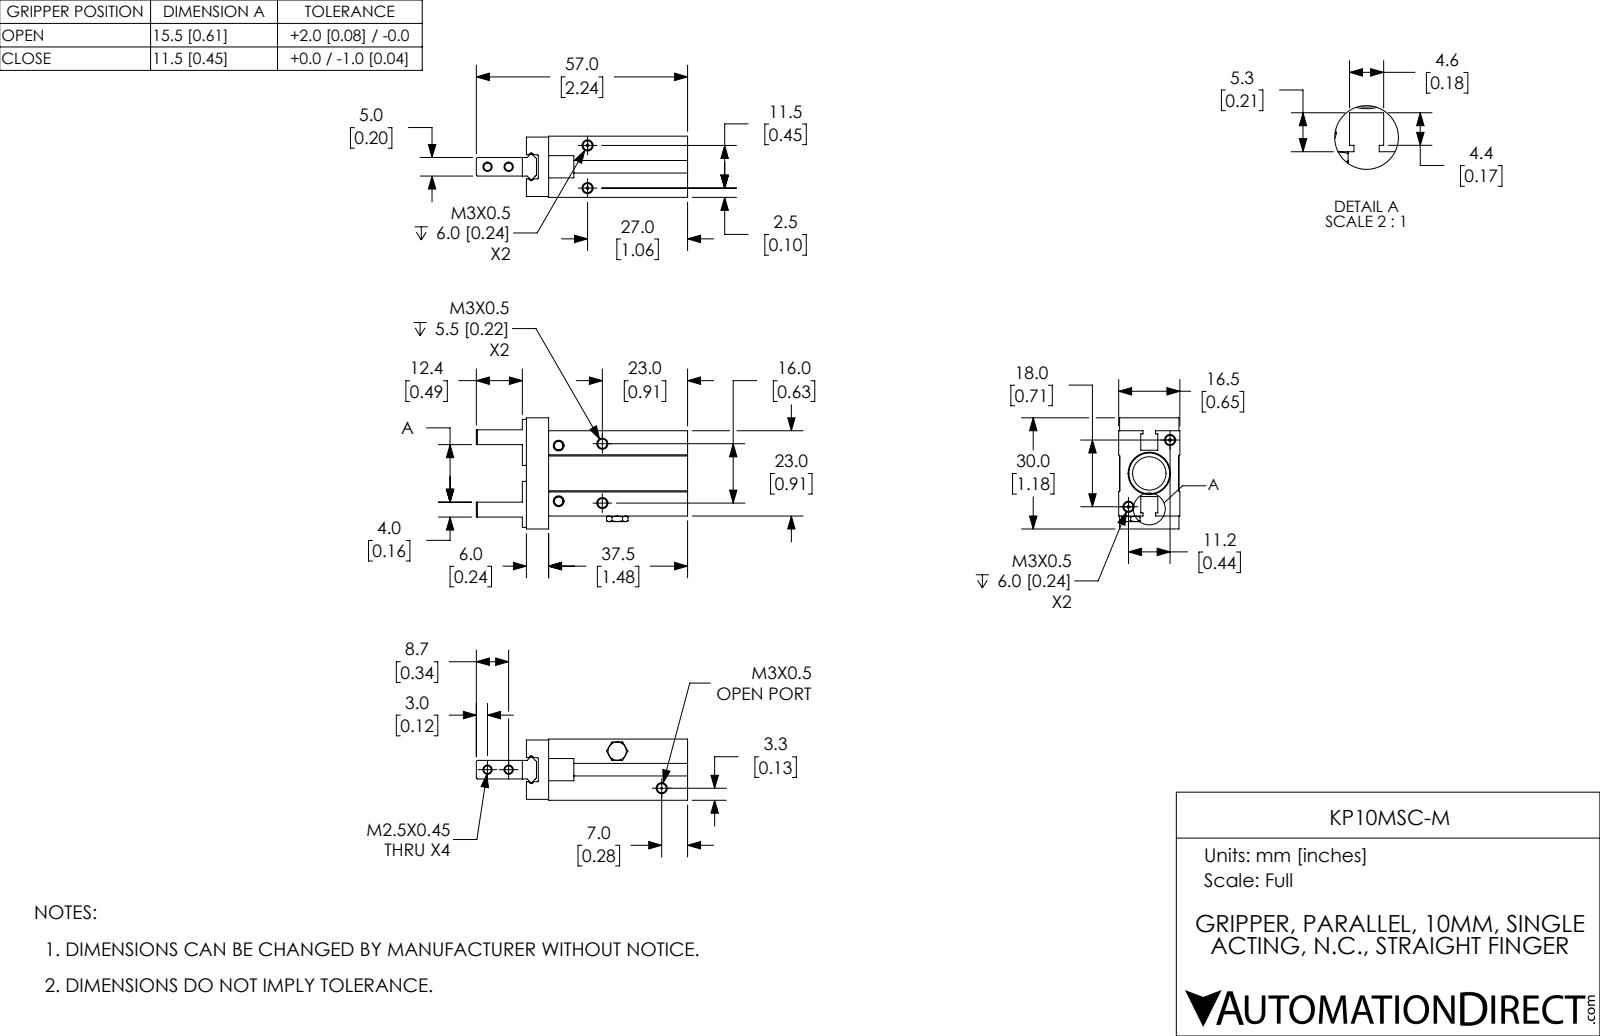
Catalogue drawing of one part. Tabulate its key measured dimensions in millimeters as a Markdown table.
| quantity | value |
| --- | --- |
| part name | KP10MSC-M; KP10MSC-M-3; KP10MSC-M-2; KP10MSC-M-1 |
| STEP written by | SolidWorks 2017 (CONFIG_CONTROL_DESIGN) |
| units | millimeters |
| bodies | 3 solids, 240 faces (118 planar, 56 cylindrical, 66 other) |
| overall size | 57 × 30 × 16.5 |
| volume | 14 374 mm³ |
| surface area | 7 494 mm² |
| round holes (diameter × count) | 2.46 × 4, 2.46 × 4, 0.5 × 2, 2.01 × 2, 3.02 × 2, 9 × 1, 11 × 1 |
| partial cylindrical surfaces (radius × count) | 0.2 × 4, 0.25 × 2, 0.75 × 2 |
| main face-to-face distances | 16.2, 5.25, 5, 5.5, 5.65, 5.95, 10.55, 10.25, 16.5, 23 |
| hole center spacings | 10.6, 22.06, 27.61, 5.7, 8.04, 11.5, 13.4, 15.62 |
